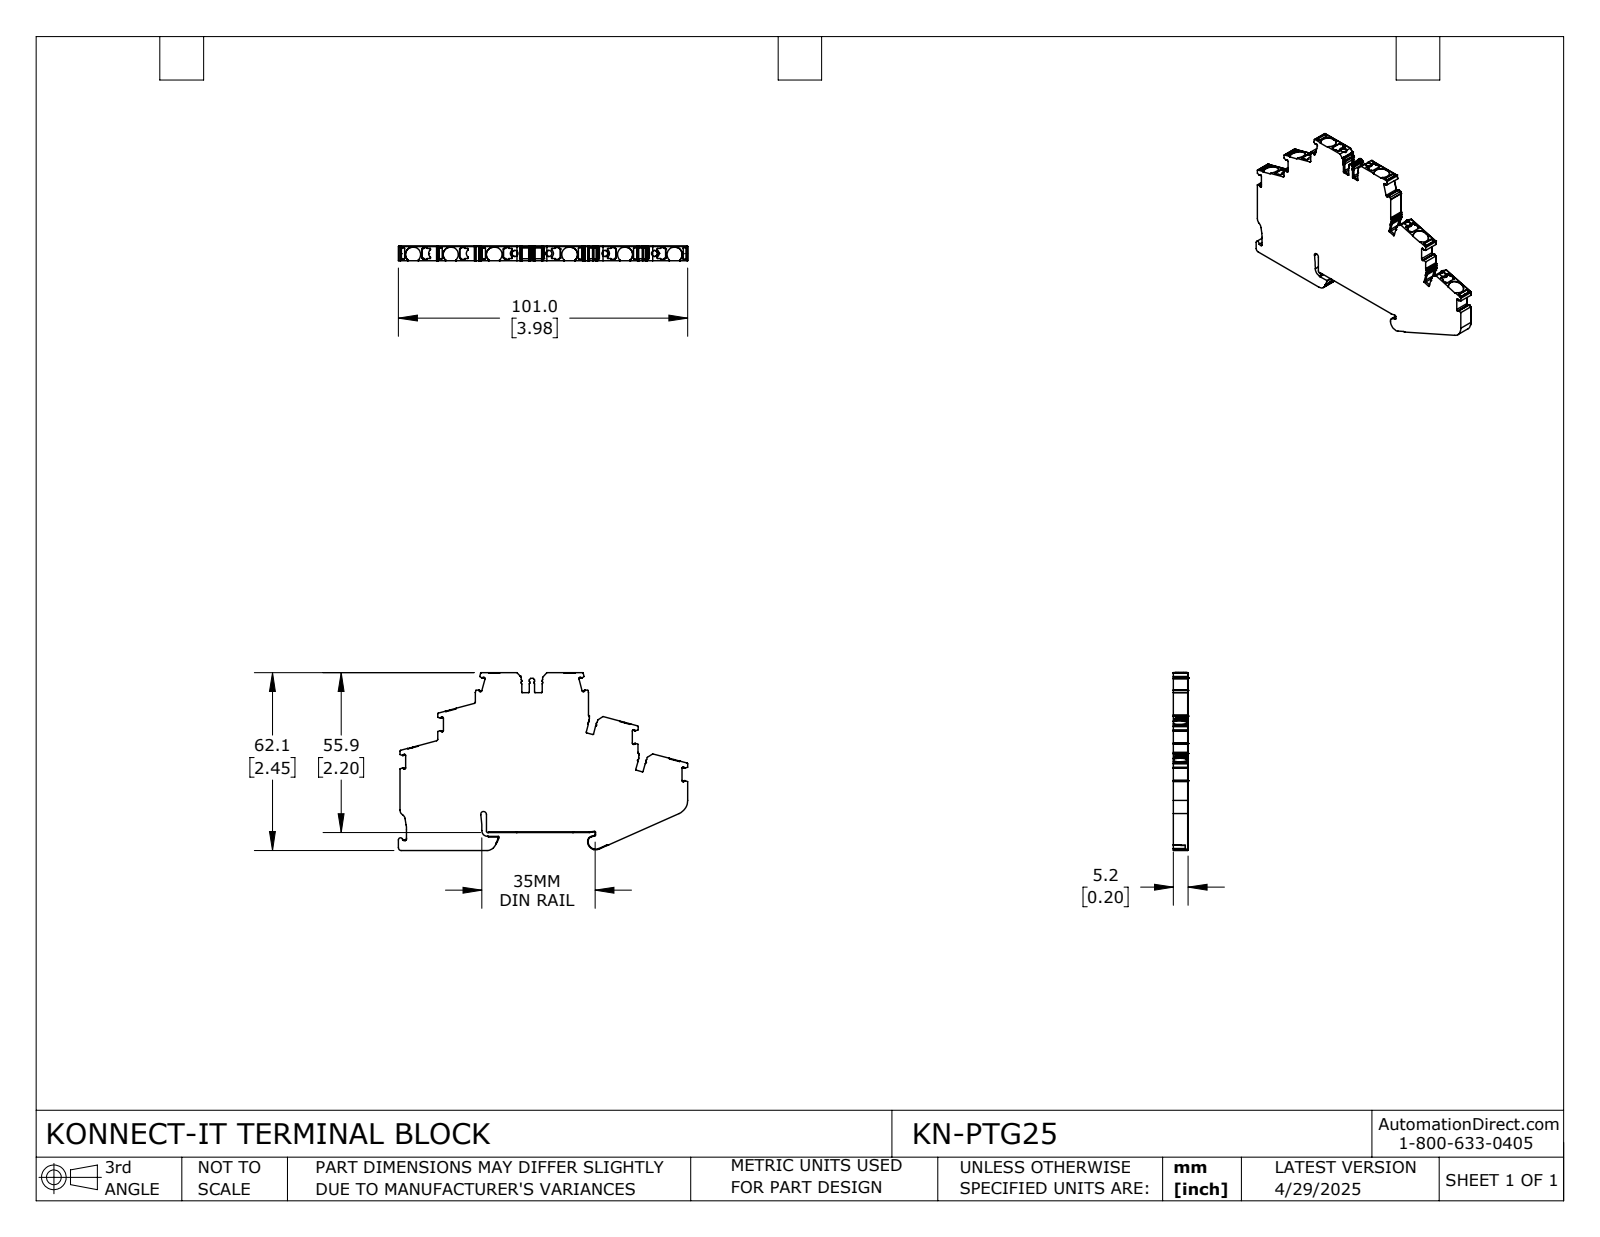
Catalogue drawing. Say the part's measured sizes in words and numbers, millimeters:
The part is named "KN-PTG25". Its 3-D file was written by "SolidWorks 2024 (CONFIG_CONTROL_DESIGN)". It is 1 solid with 1021 faces: 521 planar, 487 cylindrical and 13 other. Overall it measures 101.03 by 62.12 by 5.15 millimeters. Its volume is 22 129 cubic millimeters and its surface area 10 839 square millimeters. Round holes: 4 of diameter 2.1. Partial cylindrical surfaces (rounded edges, fillets, slot ends): 126 of radius 0.2, 47 of radius 0.3, 37 of radius 0.1, 24 of radius 0.5, 23 of radius 0.4, 14 of radius 0.6, 12 of radius 0.16, 12 of radius 0.26. The main face-to-face distances are 5.15, 55.65, 6.26, 2, 61.91, 6.46, 55.45, 8.09, 17.33, 13.17. The hole center spacings are 11.84, 20.11.
